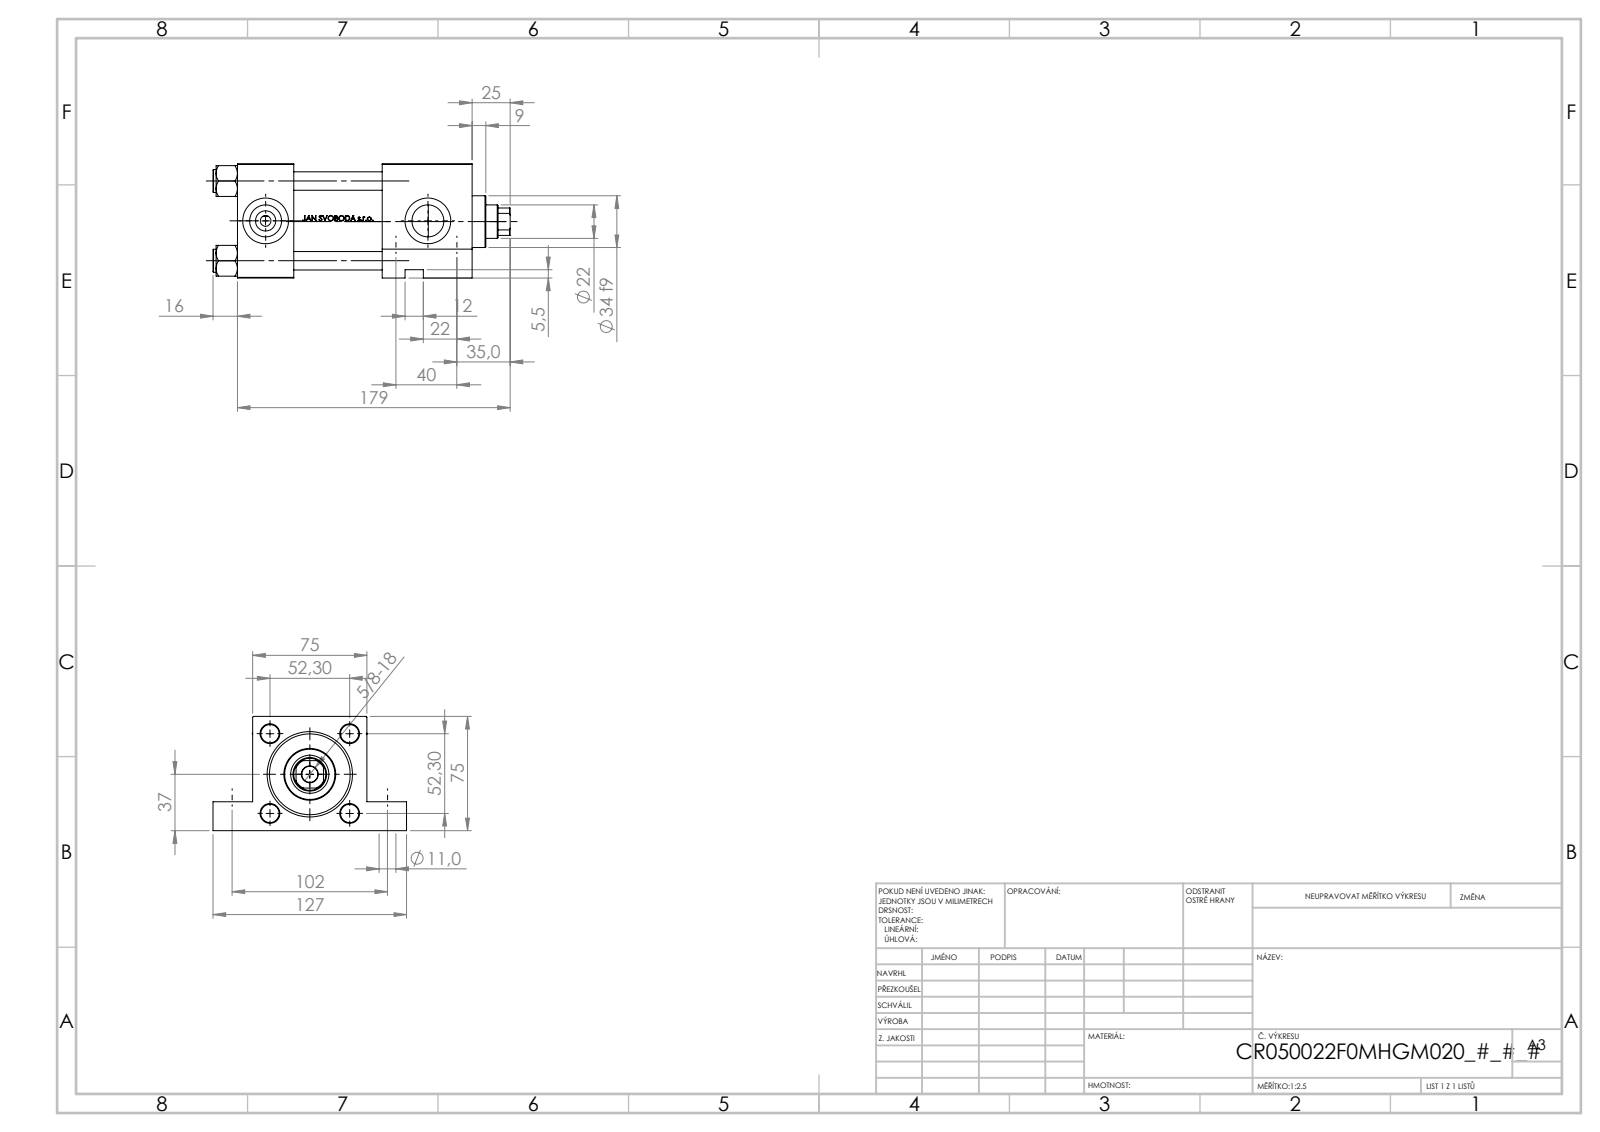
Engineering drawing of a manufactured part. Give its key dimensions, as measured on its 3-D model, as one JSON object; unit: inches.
{"part_name": "NUT_M5_F; V215_VC_A; V215CR_F_Body; V215CR_VCP_F (+1 more)", "step_written_by": "SolidWorks 2019 (CONFIG_CONTROL_DESIGN)", "units": "inches", "bodies": {"solids": 11, "faces": 1103, "planar": 437, "cylindrical": 126, "other": 540}, "overall_size": [7.677, 5, 2.953], "volume_in3": 43.11, "surface_area_in2": 242, "round_holes": [[0.472, 4], [0.276, 2], [0.433, 2], [0.433, 2], [0.825, 2], [1.181, 2], [0.413, 1], [0.866, 1], [0.984, 1], [1.614, 1], [1.969, 1], [2.087, 1]], "round_bosses_or_shafts": [[0.591, 4], [2.205, 1], [1.339, 1]], "partial_cylinders_radius": [[0.413, 1]], "face_to_face_distances": [2.953, 1.457, 4.606, 6.063, 3.74, 2.283, 2.323, 0.748, 2.205, 4.933], "hole_center_spacings": [2.059, 1.442, 1.47, 1.575, 2.912, 4.016, 4.313, 4.193]}
